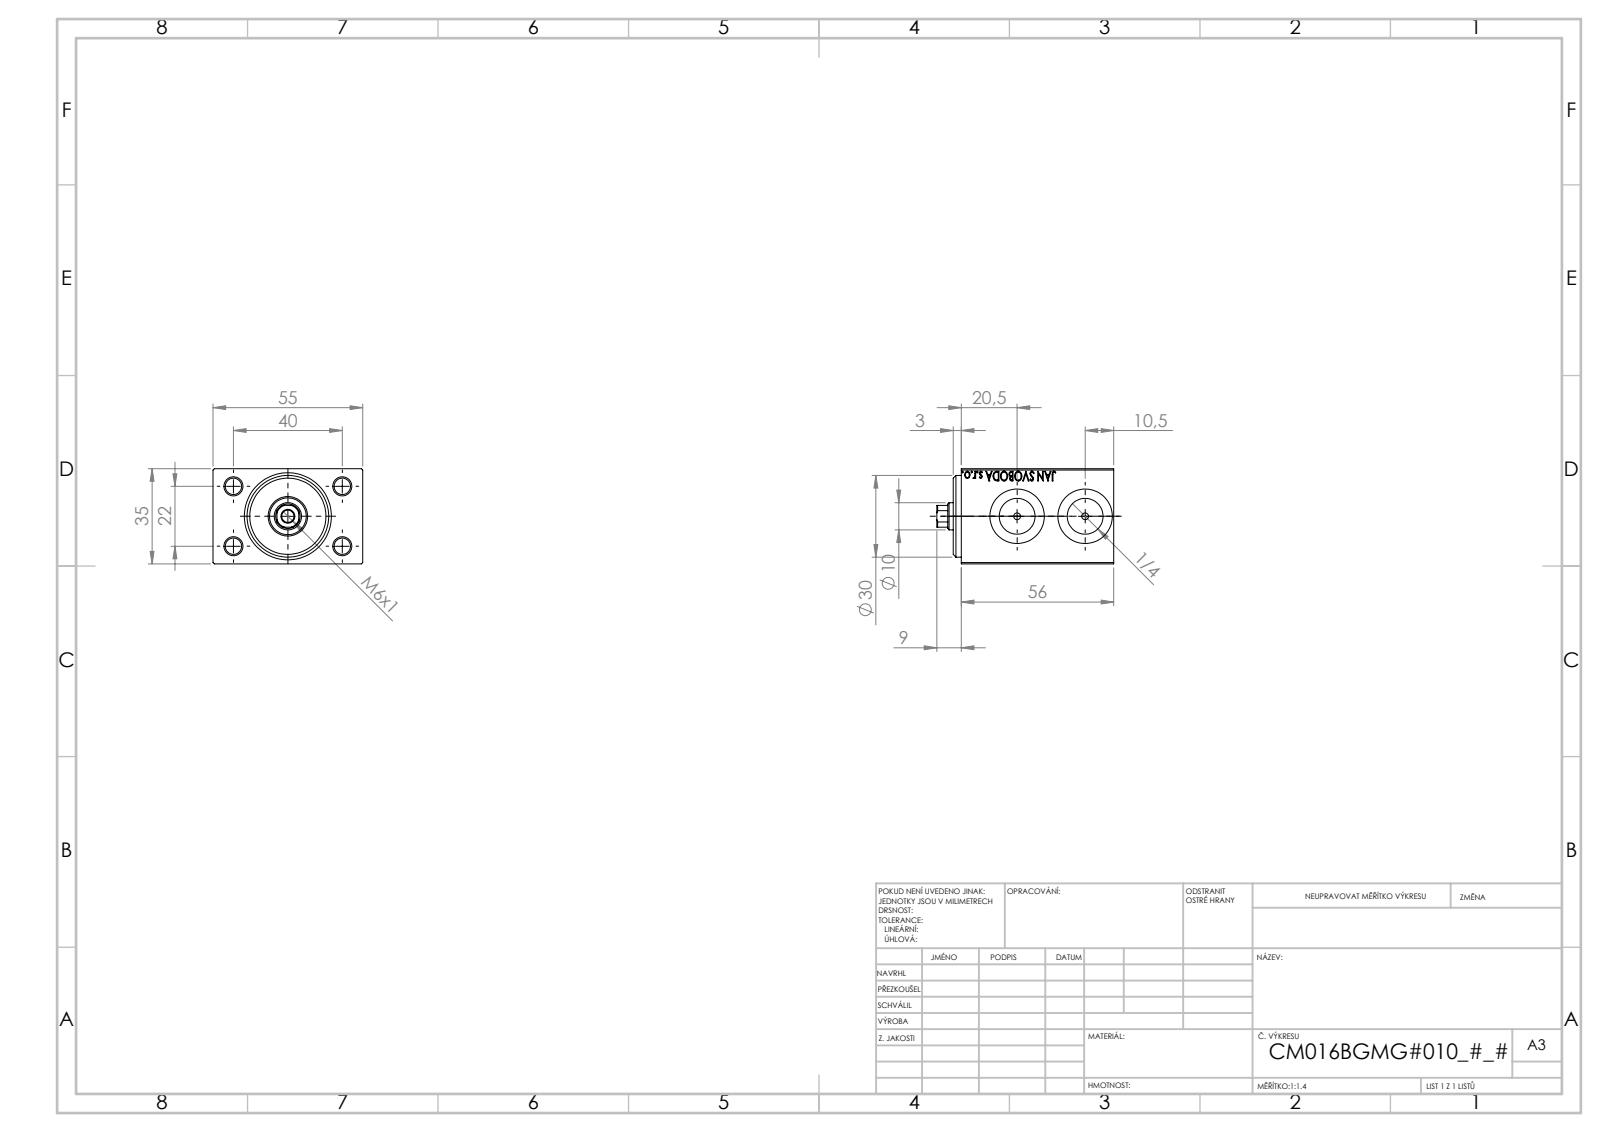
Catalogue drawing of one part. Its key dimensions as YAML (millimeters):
part_name: "V450CM_B_Body; V450CM_VC_B; V450CM_B_VCP"
step_written_by: "SolidWorks 2019 (CONFIG_CONTROL_DESIGN)"
units: millimeters
bodies: {solids: 3, faces: 881, planar: 401, cylindrical: 54, other: 426}
overall_size: [65, 55, 35]
volume: 102528
surface_area: 25989
round_holes:
  - {diameter: 6, count: 4}
  - {diameter: 2.5, count: 2}
  - {diameter: 13.16, count: 2}
  - {diameter: 20, count: 2}
  - {diameter: 4.5, count: 1}
  - {diameter: 10, count: 1}
  - {diameter: 13.5, count: 1}
  - {diameter: 14.5, count: 1}
  - {diameter: 16, count: 1}
  - {diameter: 18, count: 1}
  - {diameter: 30, count: 1}
partial_cylinders:
  - {radius: 4.5, count: 1}
face_to_face_distances: [35, 5, 51, 55, 56, 8, 3, 59, 54, 46]
hole_center_spacings: [22.83, 22, 40, 45.65, 25]
